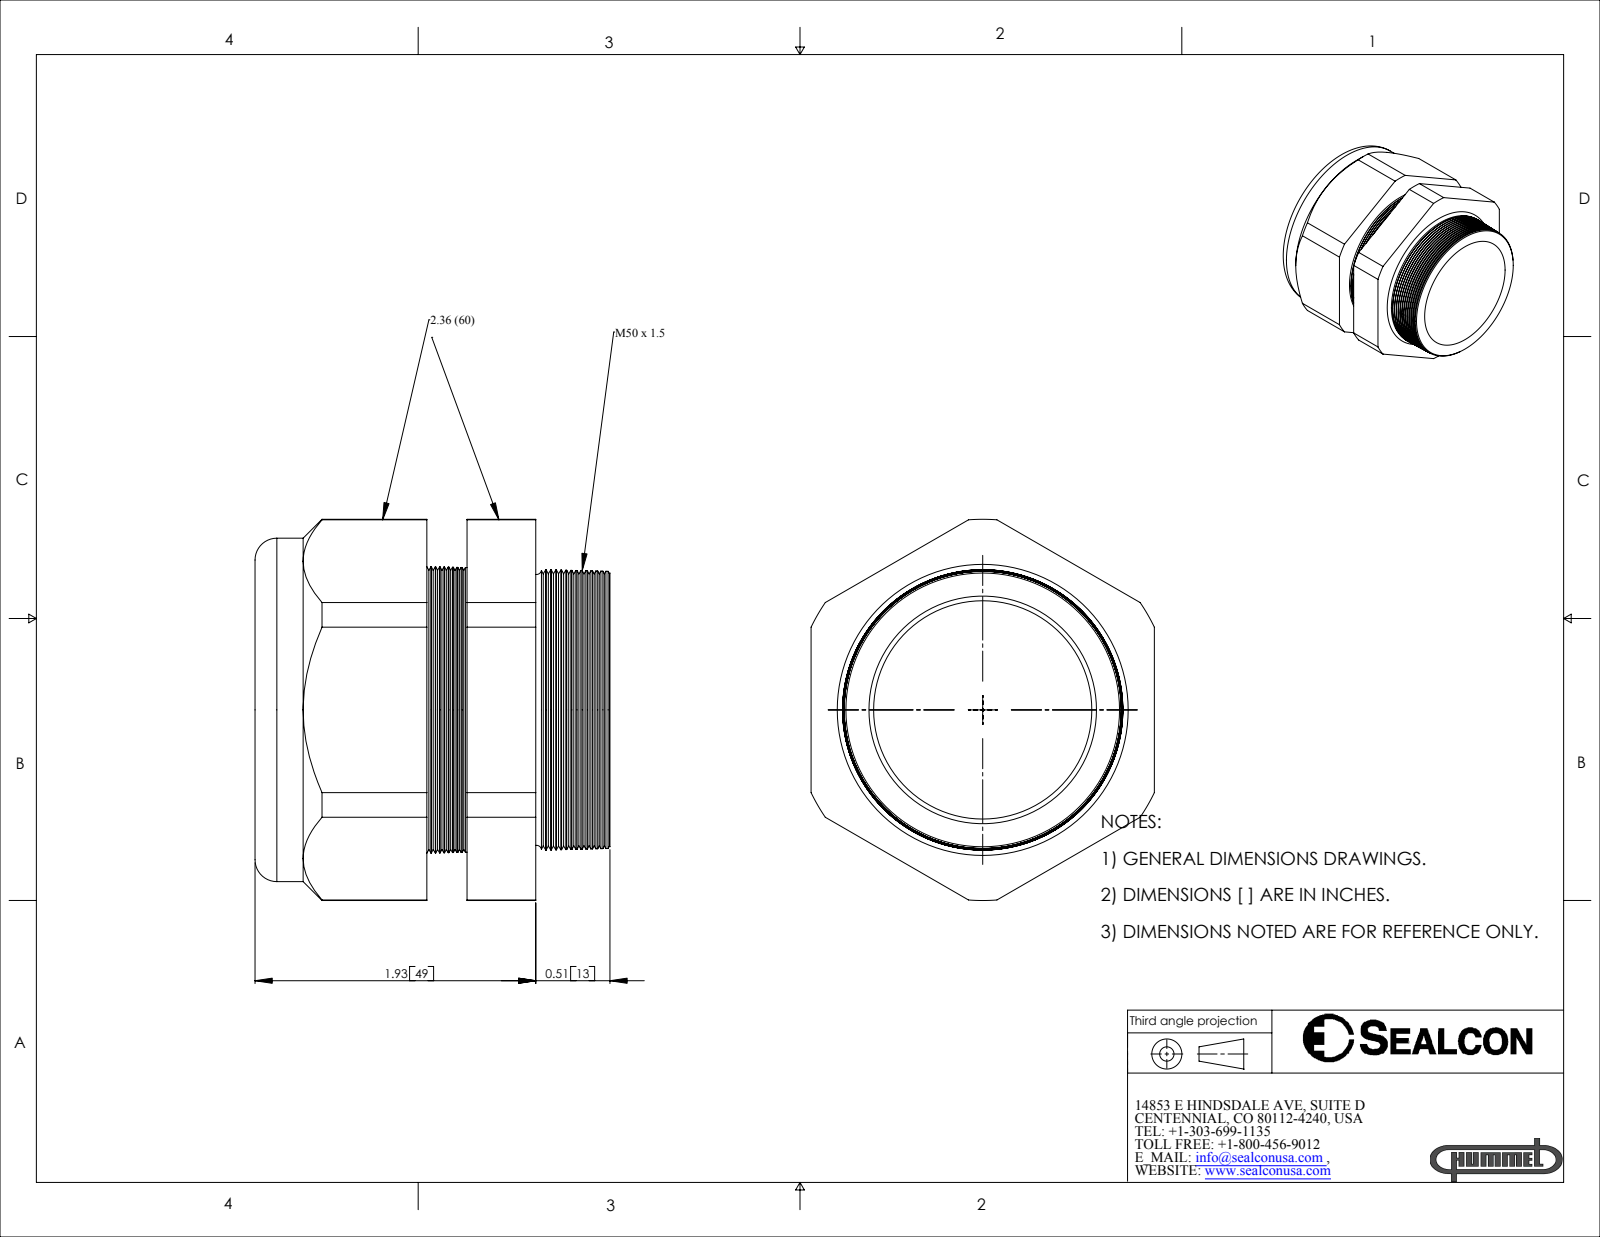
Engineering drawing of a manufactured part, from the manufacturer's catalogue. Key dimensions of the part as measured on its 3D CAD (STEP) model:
Part name (STEP PRODUCT): CD50MP-GY
STEP written by: SolidWorks 2007 (CONFIG_CONTROL_DESIGN)
Units: inches
Bodies: 2 solids, 190 faces (20 planar, 20 cylindrical, 150 other)
Overall size (bounding box): 2.62 × 2.44 × 2.36
Volume: 6.336 in³ · Surface area: 47.67 in²
Round holes (diameter × count): ⌀1.48 ×1, ⌀1.5 ×1
Round bosses / shafts (diameter × count): ⌀2.36 ×1
Partial cylindrical surfaces — rounded edges, fillets, slot ends (radius × count): R1.31 ×1
Main face-to-face distances: 2.36, 1.008, 0.731, 0.276, 0.43, 1.161, 1.438, 1.91, 1.48, 0.749
